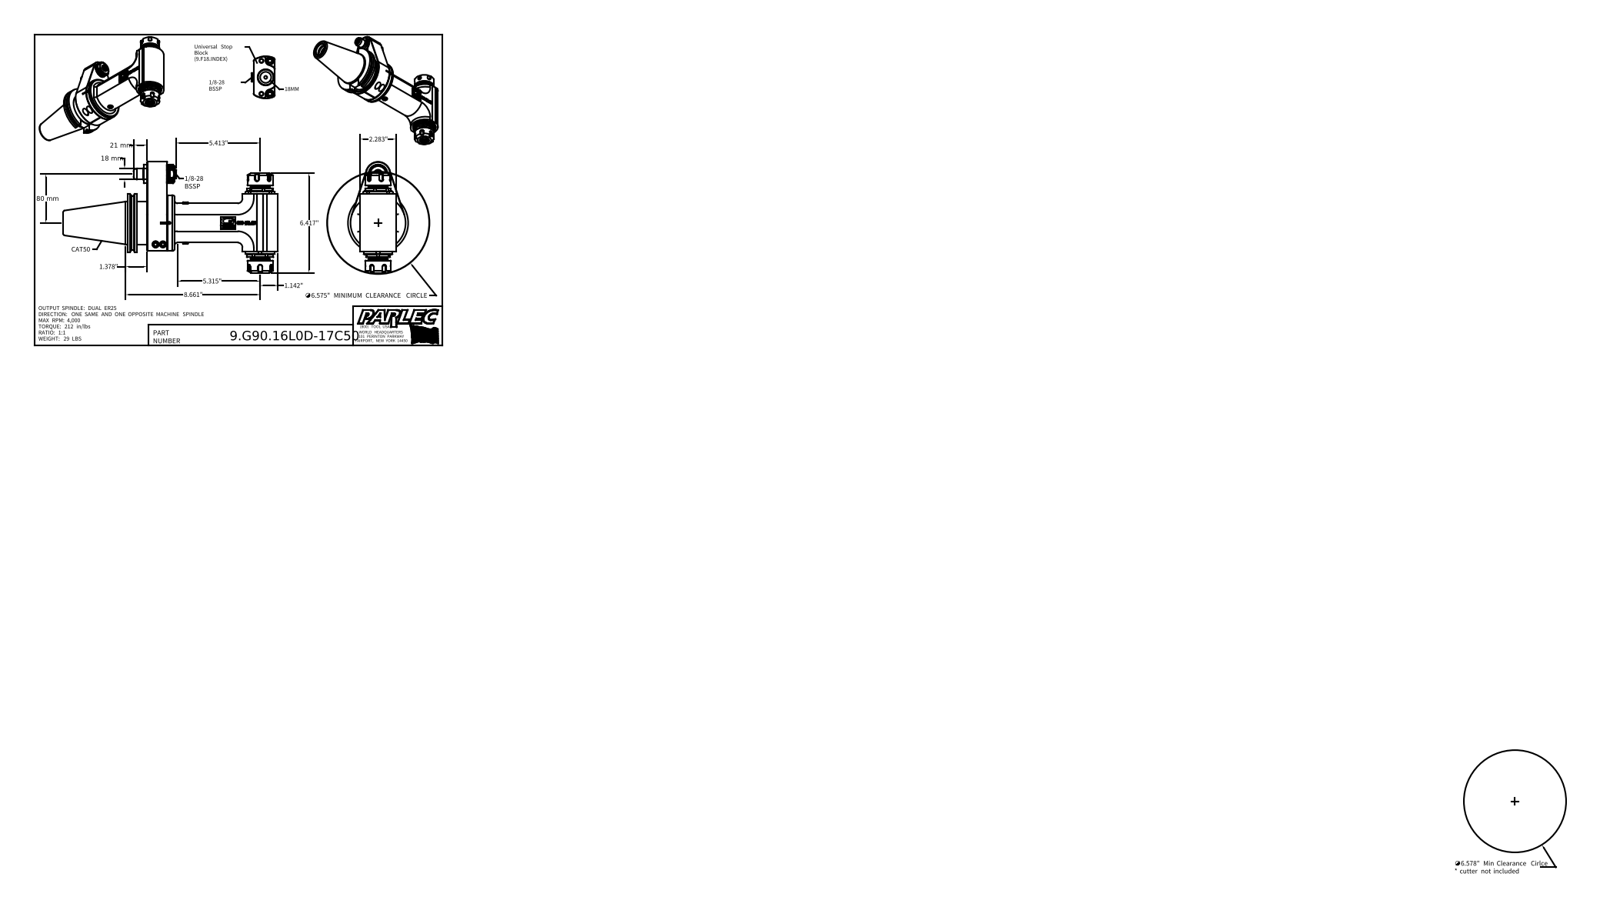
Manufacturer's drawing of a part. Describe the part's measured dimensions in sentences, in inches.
The part is named "9.G90.16L0D-17C50; 9_GA1_458_1 (Classic, Type 1, Cat50, 80mm); 9_G90_16LD". Its 3-D file was written by "Autodesk Inventor 2022 (AUTOMOTIVE_DESIGN)". It is 45 solids with 1531 faces: 707 planar, 310 cylindrical and 514 other. Overall it measures 13.811 by 7.146 by 3.875 inches. Its volume is 80.98 cubic inches and its surface area 358.7 square inches. Round holes: 8 of diameter 0.165, 6 of diameter 0.236, 4 of diameter 0.197, 3 of diameter 0.335, 2 of diameter 0.157, 2 of diameter 0.276, 2 of diameter 0.413, 2 of diameter 0.433, 2 of diameter 1.201, 2 of diameter 1.654, 1 of diameter 0.13, 1 of diameter 0.551. Round bosses or shafts: 3 of diameter 0.394, 3 of diameter 0.157, 2 of diameter 0.315, 1 of diameter 3.875, 1 of diameter 3.593, 1 of diameter 3.543, 1 of diameter 3.071, 1 of diameter 2.75. Partial cylindrical surfaces (rounded edges, fillets, slot ends): 17 of radius 0.118, 16 of radius 0.059, 8 of radius 0.049, 3 of radius 0.098, 3 of radius 1.26, 2 of radius 0.085, 2 of radius 0.197, 1 of radius 0.079. The main face-to-face distances are 1.299, 0.626, 0.197, 0.354, 2.283, 1.252, 1.925, 2.551, 1.378, 0.984. The hole center spacings are 1.476, 0.764, 2.088, 2.557, 2.852, 0.366, 0.433, 0.591.
